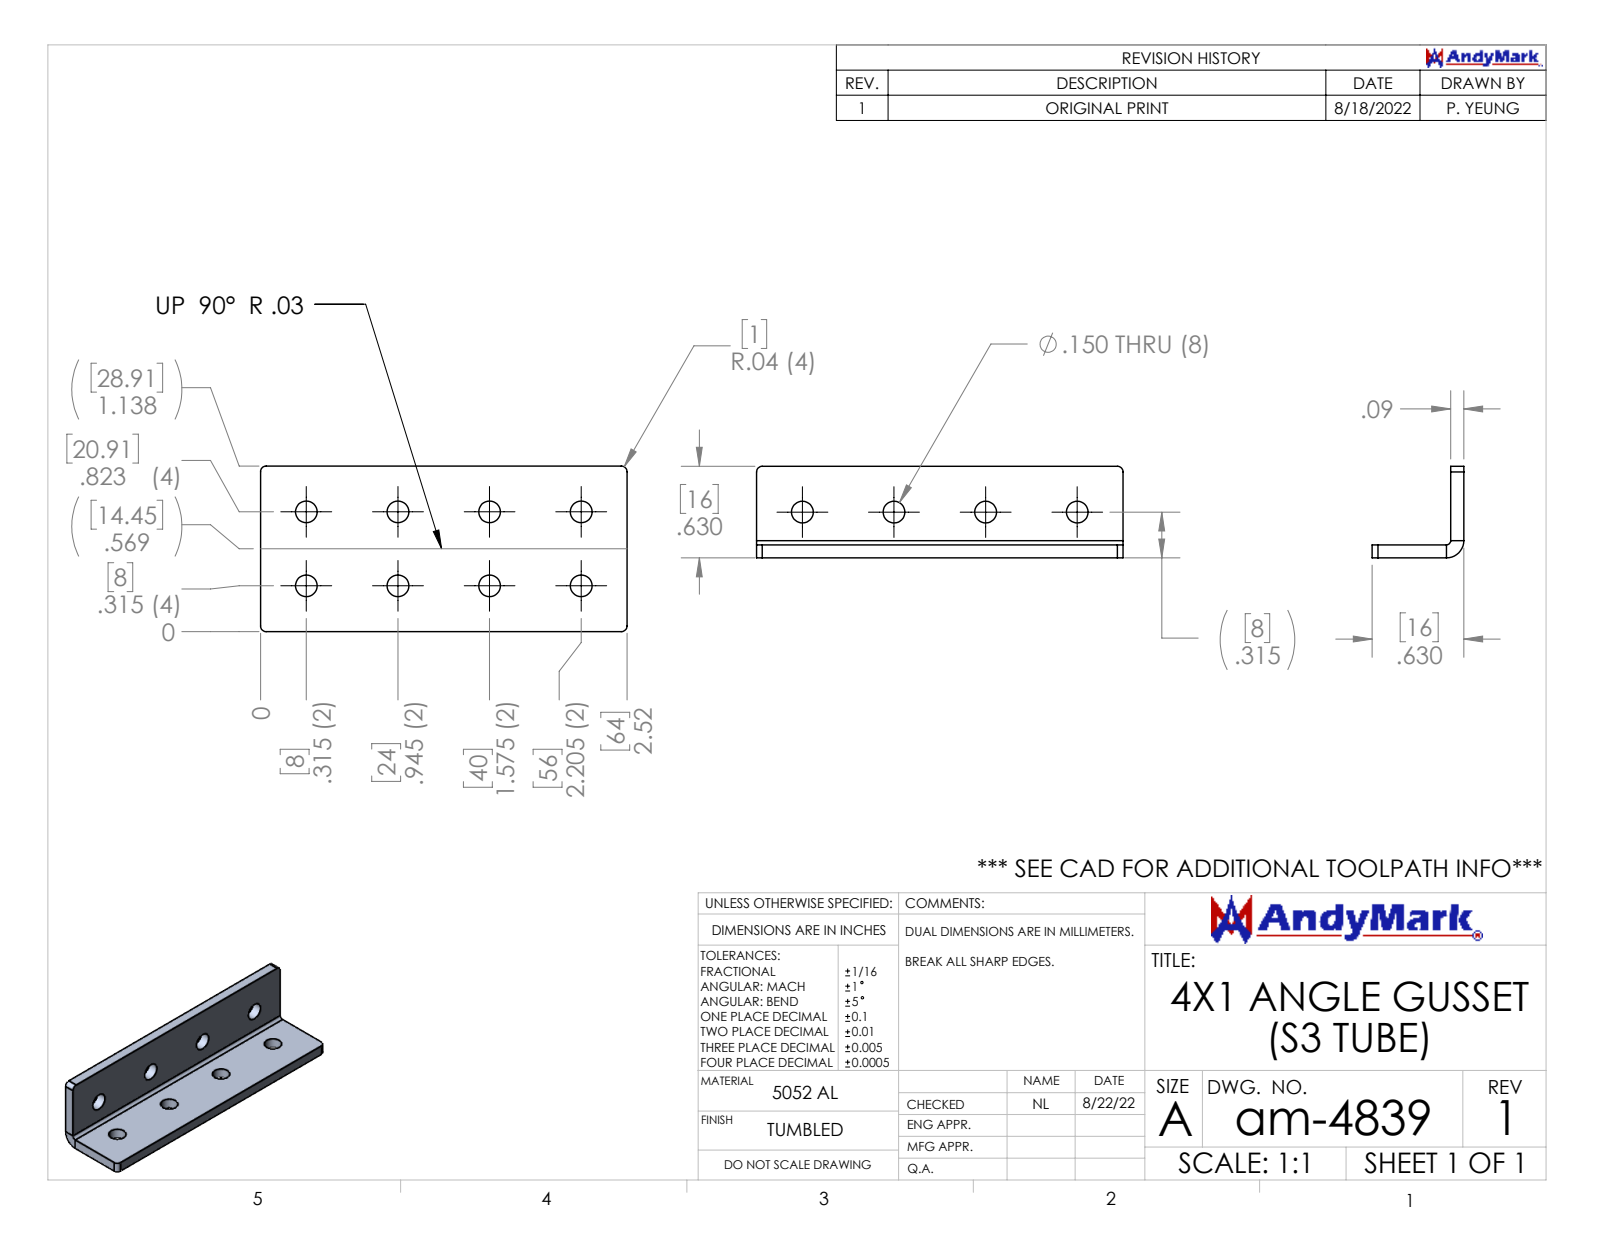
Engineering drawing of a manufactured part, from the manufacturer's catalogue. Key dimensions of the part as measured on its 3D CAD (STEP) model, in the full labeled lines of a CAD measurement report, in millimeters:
Part name (STEP PRODUCT): am-4839 4x1 Angle Gusset
STEP written by: SolidWorks 2022 (CONFIG_CONTROL_DESIGN)
Units: millimetres
Bodies: 1 solid, 34 faces (12 planar, 22 cylindrical, 0 other)
Overall size (bounding box): 64 × 16 × 16
Volume: 4 010 mm³ · Surface area: 4 156 mm²
Round holes (diameter × count): ⌀3.8 ×8
Partial cylindrical surfaces — rounded edges, fillets, slot ends (radius × count): R1 ×4, R0.7 ×1, R3 ×1
Main face-to-face distances: 2.3, 16, 13.7, 64
Hole centre spacings: 16, 32, 48
